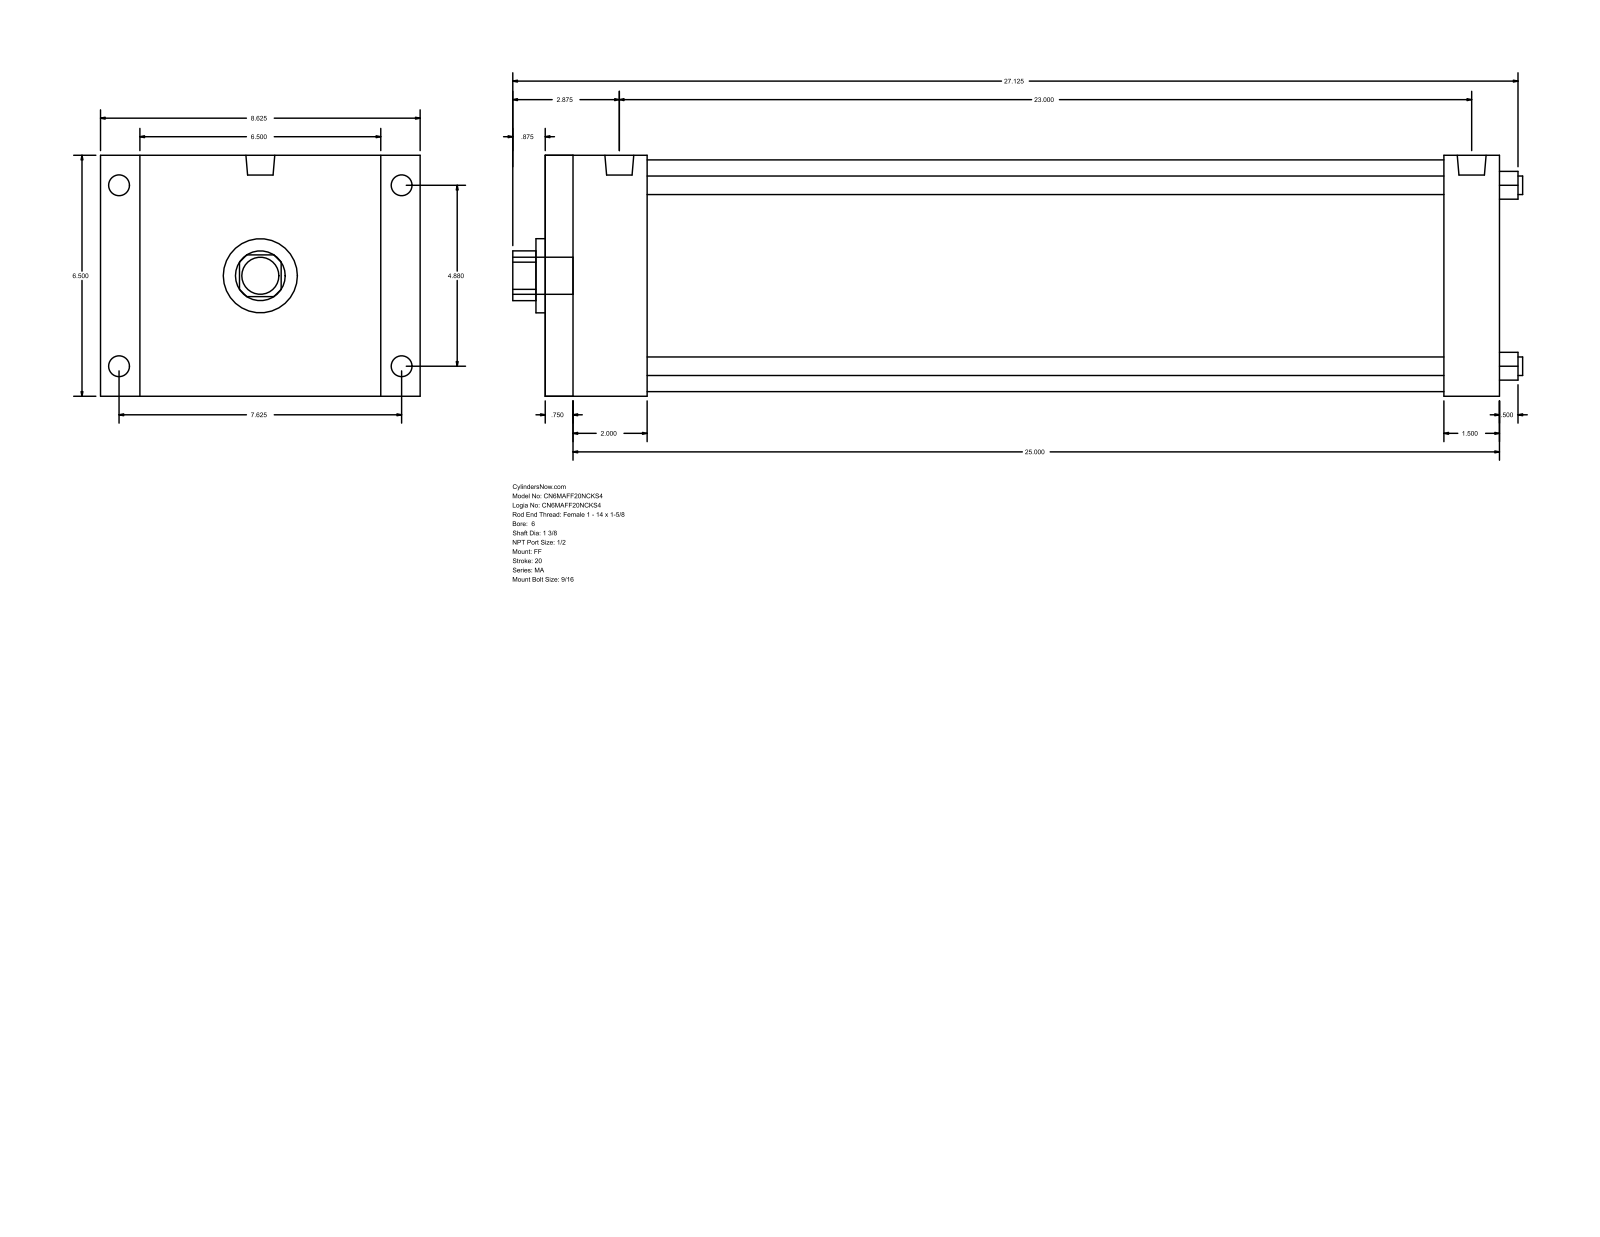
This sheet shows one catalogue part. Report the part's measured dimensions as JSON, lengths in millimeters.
{"part_name": "MA_FF__0600_1.375", "step_written_by": "GSSL Pune (CONFIG_CONTROL_DESIGN)", "units": "millimeters", "bodies": {"solids": 0, "faces": 92, "planar": 64, "cylindrical": 28, "other": 0}, "overall_size": [692.15, 219.07, 165.1], "round_holes": [[12.7, 4], [34.92, 1], [50.8, 1], [158.75, 1]], "round_bosses_or_shafts": [[17.46, 4], [14.29, 4], [19.77, 2], [25.4, 1]], "partial_cylinders_radius": [[17.06, 1]], "face_to_face_distances": [165.1, 654.04, 638.17, 15.87, 38.1, 66.67, 50.8, 587.37, 615.94, 600.07], "hole_center_spacings": [87.65, 123.96, 175.31]}
